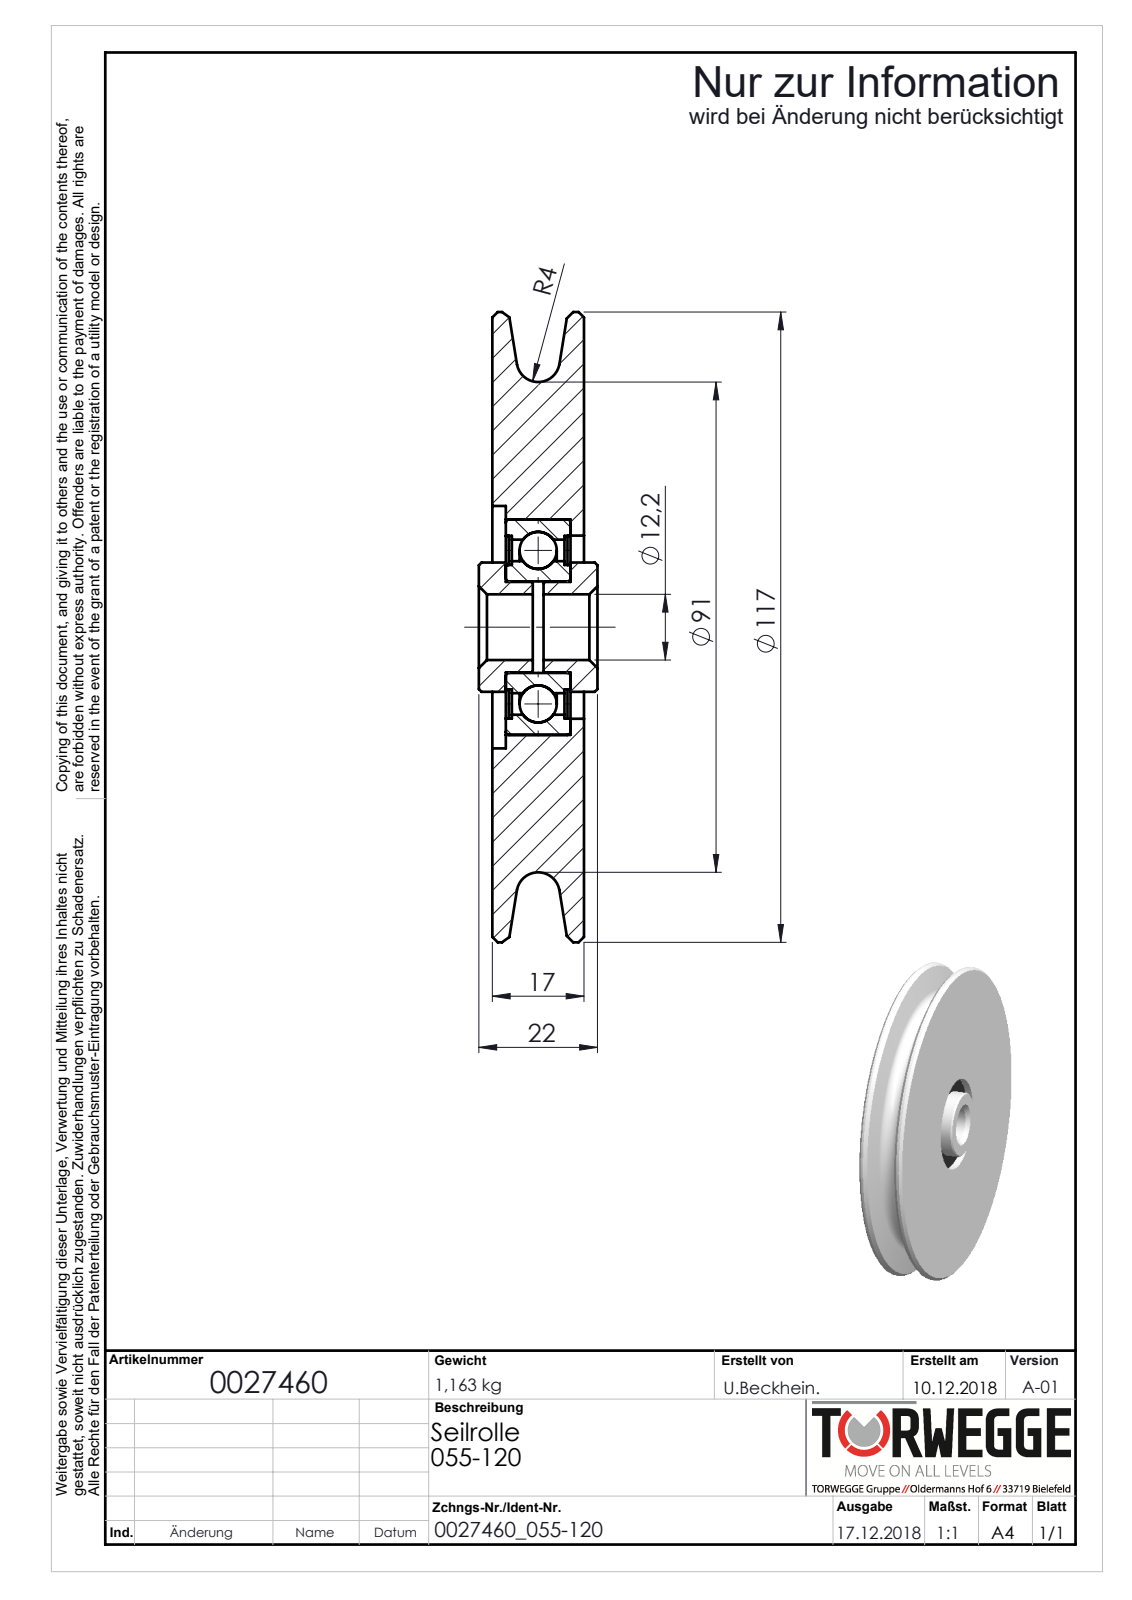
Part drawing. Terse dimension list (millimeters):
name: 0027460_055-120_(A-01)
written by: SolidWorks 2018 (AUTOMOTIVE_DESIGN)
unit: mm
bodies: 8 solids, 118 faces (22 planar, 50 cylindrical, 46 other)
size: 117 × 117 × 22
volume: 138 710 mm³; area: 46 160 mm²
holes: 1× ⌀12.2, 1× ⌀17, 1× ⌀23.1, 1× ⌀32.5, 1× ⌀33.91, 1× ⌀34, 1× ⌀40, 1× ⌀45
bosses: 1× ⌀117, 1× ⌀24.5, 1× ⌀24, 1× ⌀16.8
face distances: 17, 2.5, 14.5, 12, 0.56, 3.06, 13.94, 11.44, 10.88, 5
